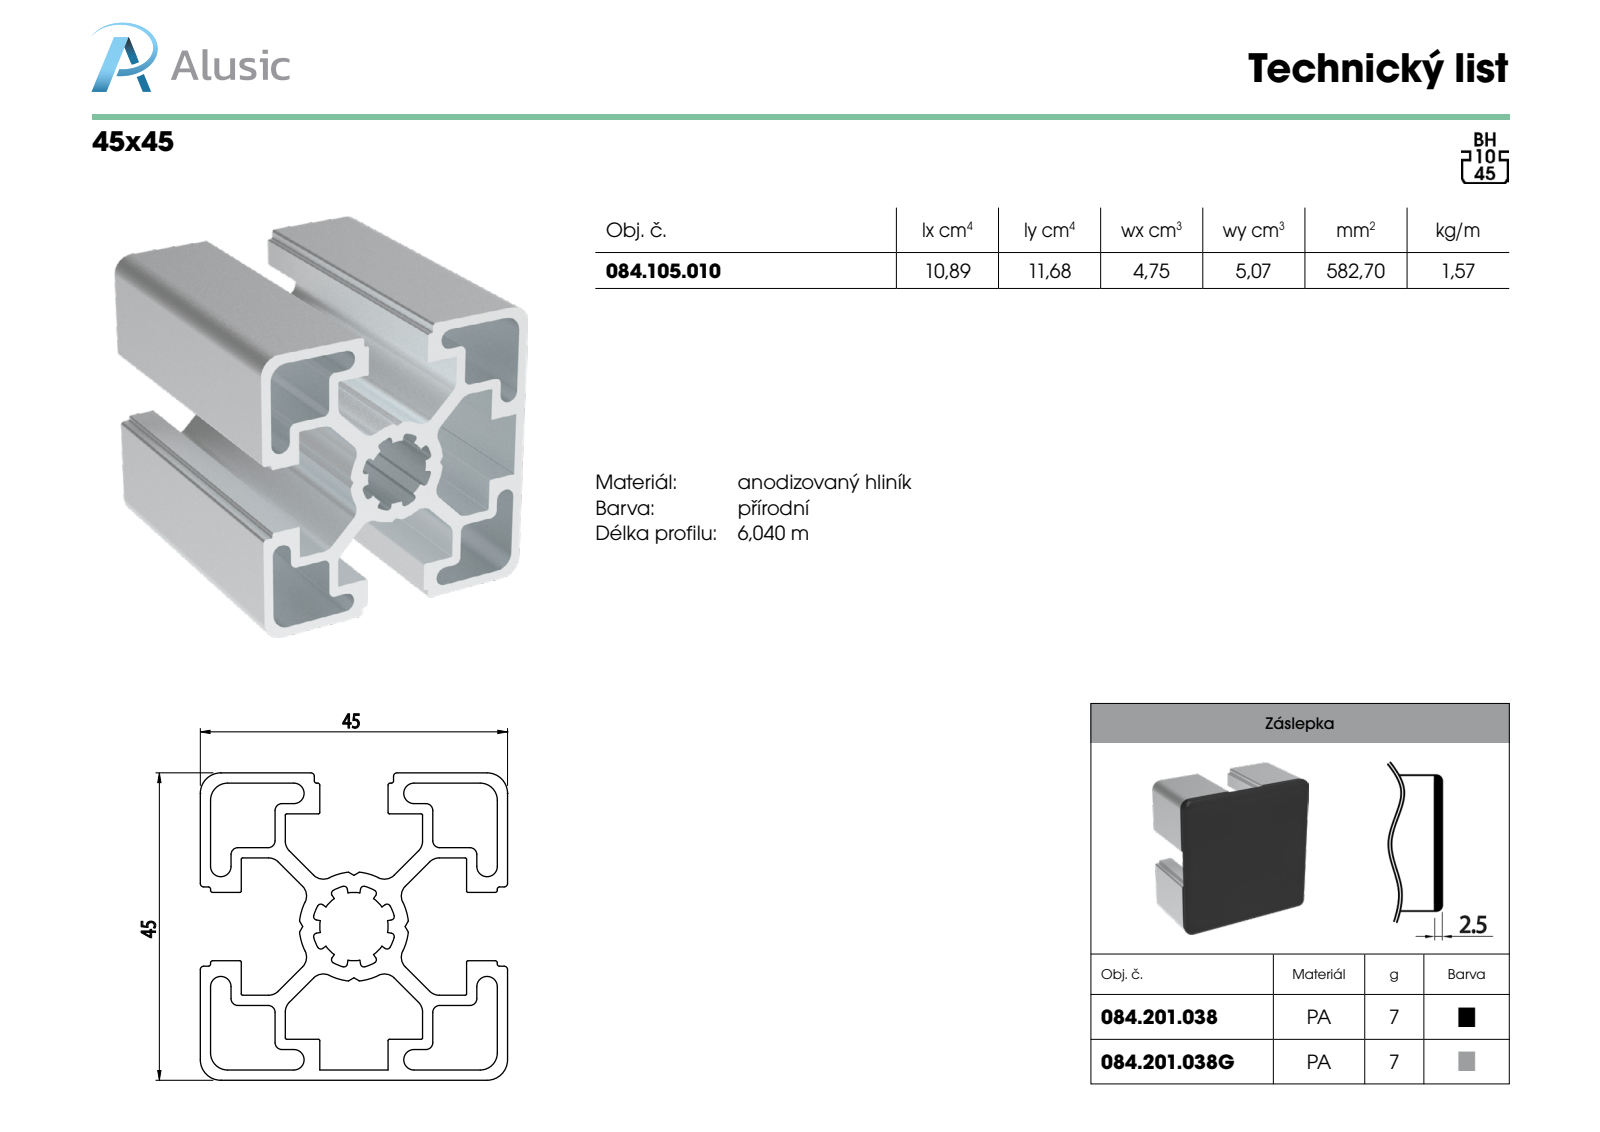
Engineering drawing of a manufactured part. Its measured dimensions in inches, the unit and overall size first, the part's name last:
Units: inches
Overall size (bounding box): 3.937 × 1.772 × 1.772
Partial cylindrical surfaces — rounded edges, fillets, slot ends (radius × count): R0.02 ×22, R0.008 ×16, R0.079 ×16, R0.012 ×12, R0.039 ×12, R0.059 ×8, R0.098 ×4, R0.118 ×4
Main face-to-face distances: 0.059, 1.713, 0.431, 1.281, 1.772, 0.177, 1.535, 1.104, 0.254, 1.654
Volume: 3.556 in³ · Surface area: 97.93 in²
Bodies: 1 solid, 229 faces (102 planar, 127 cylindrical, 0 other)
Part name (STEP PRODUCT): 084.105.10
STEP written by: SolidWorks 2018 (AUTOMOTIVE_DESIGN)
